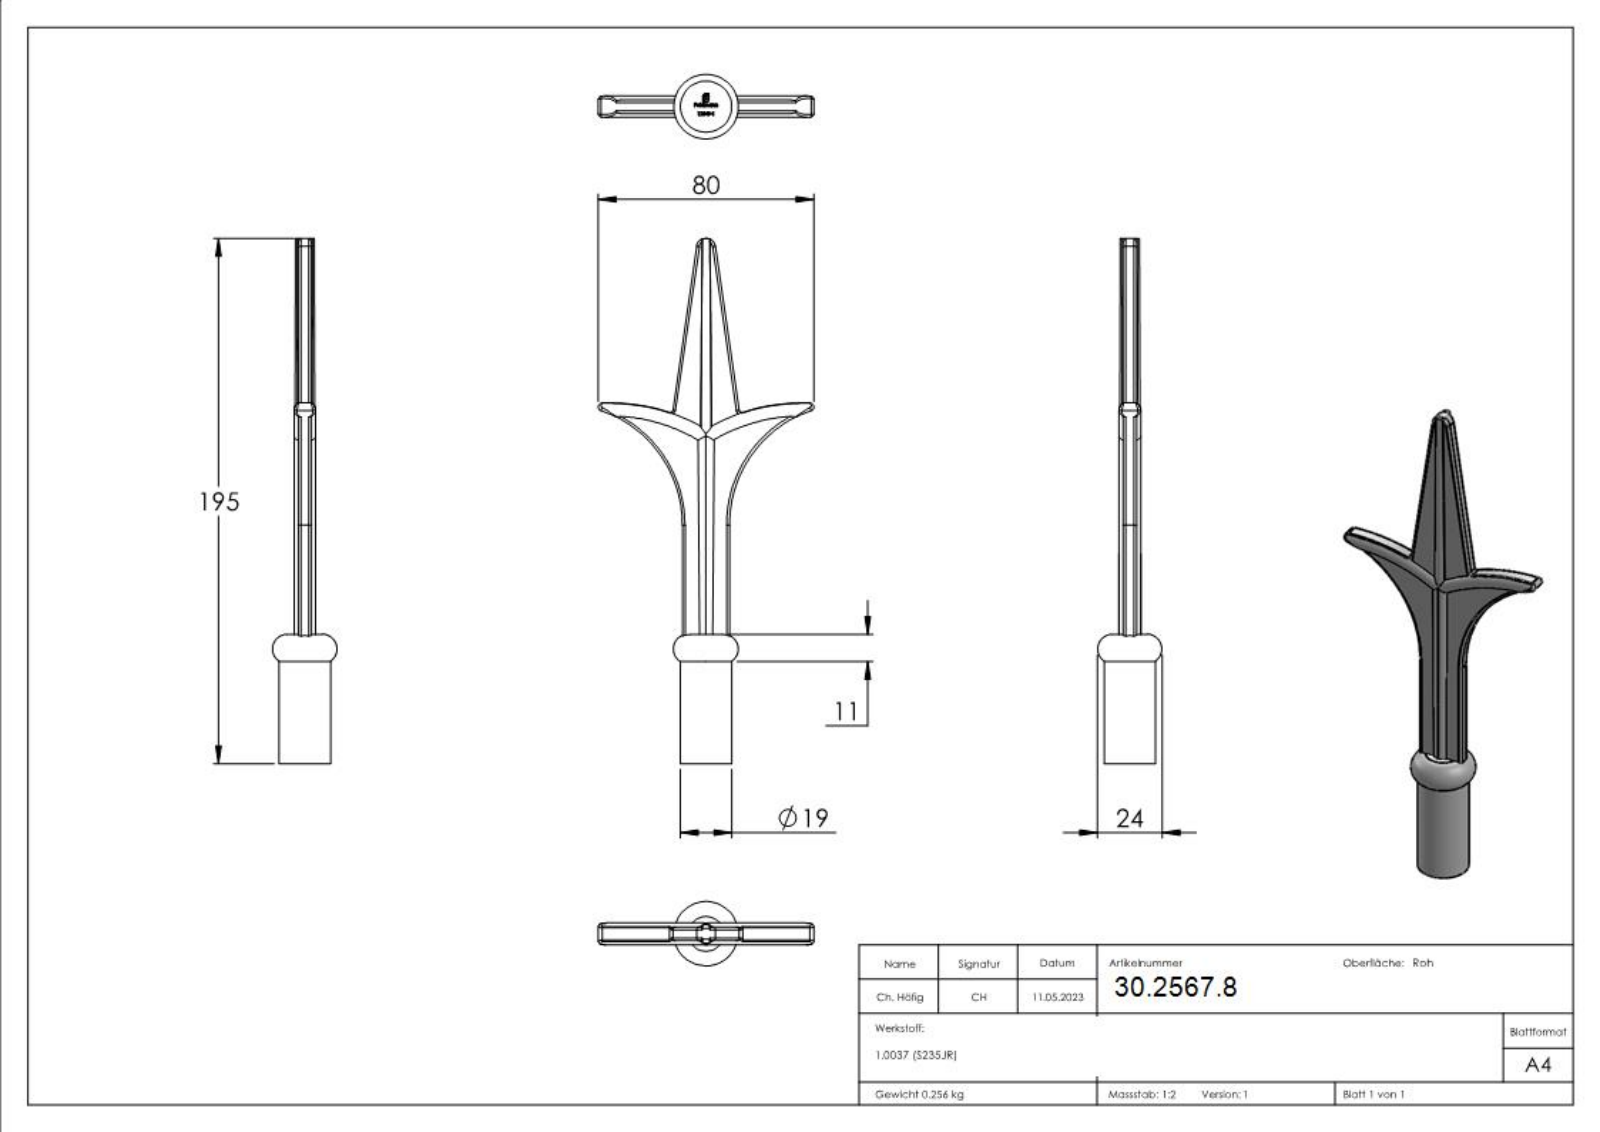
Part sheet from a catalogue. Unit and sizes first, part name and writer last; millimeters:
Units: millimetres
Overall size (bounding box): 195 × 80 × 24
Round bosses / shafts (diameter × count): ⌀19 ×1
Partial cylindrical surfaces — rounded edges, fillets, slot ends (radius × count): R1 ×10, R1.5 ×2, R45 ×2, R70 ×2, R3.54 ×1
Main face-to-face distances: 5, 17.5, 48, 47.9, 1.7, 0.34, 1.53, 1.82, 1.57, 0.44
Volume: 32 815 mm³ · Surface area: 12 176 mm²
Bodies: 1 solid, 306 faces (151 planar, 18 cylindrical, 137 other)
Part name (STEP PRODUCT): 126-B-1
STEP written by: SolidWorks 2018 (CONFIG_CONTROL_DESIGN)
